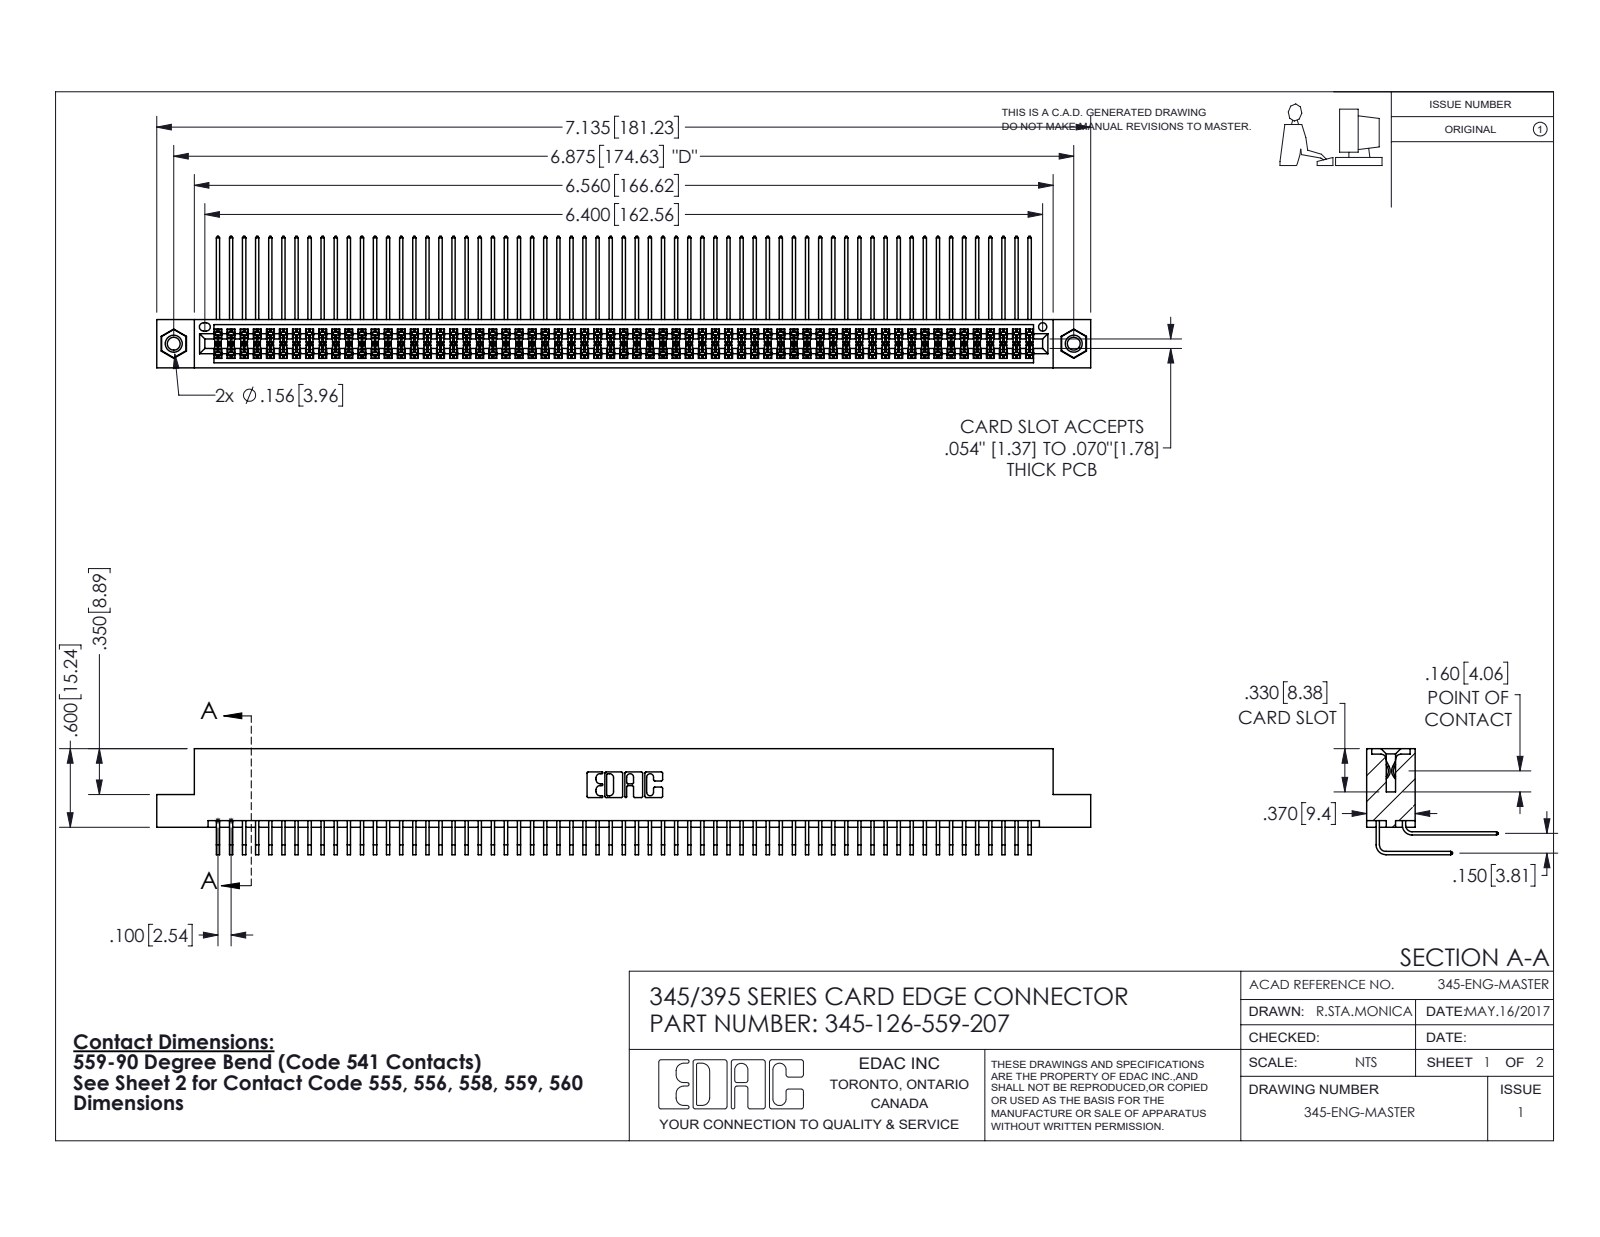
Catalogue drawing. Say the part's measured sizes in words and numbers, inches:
The part is named "345-292-001_558 559 Tail - 1; 345-126-559-207; 345-250-001_345-250-005-103; 345 Part_Flush Mounting Lugs - 0.156 Dia-TI (+1 more)". Its 3-D file was written by "SolidWorks 2016 (CONFIG_CONTROL_DESIGN)". It is 129 solids with 6738 faces: 4522 planar, 2200 cylindrical and 16 other. Overall it measures 7.135 by 1.005 by 0.809 inches. Its volume is 1.13 cubic inches and its surface area 48.39 square inches. Round holes: 2 of diameter 0.098, 2 of diameter 0.125, 2 of diameter 0.156, 1 of diameter 0.064. Round bosses or shafts: 2 of diameter 0.155. Partial cylindrical surfaces (rounded edges, fillets, slot ends): 251 of radius 0.006, 22 of radius 0.01, 6 of radius 0.007, 6 of radius 0.031, 3 of radius 0.026, 2 of radius 0.014, 2 of radius 0.019, 2 of radius 0.022. The main face-to-face distances are 0.072, 0.298, 0.2, 0.37, 0.098, 0.272, 0.025, 0.225, 0.175, 0.15. The hole center spacings are 0.27, 6.639, 6.875.
